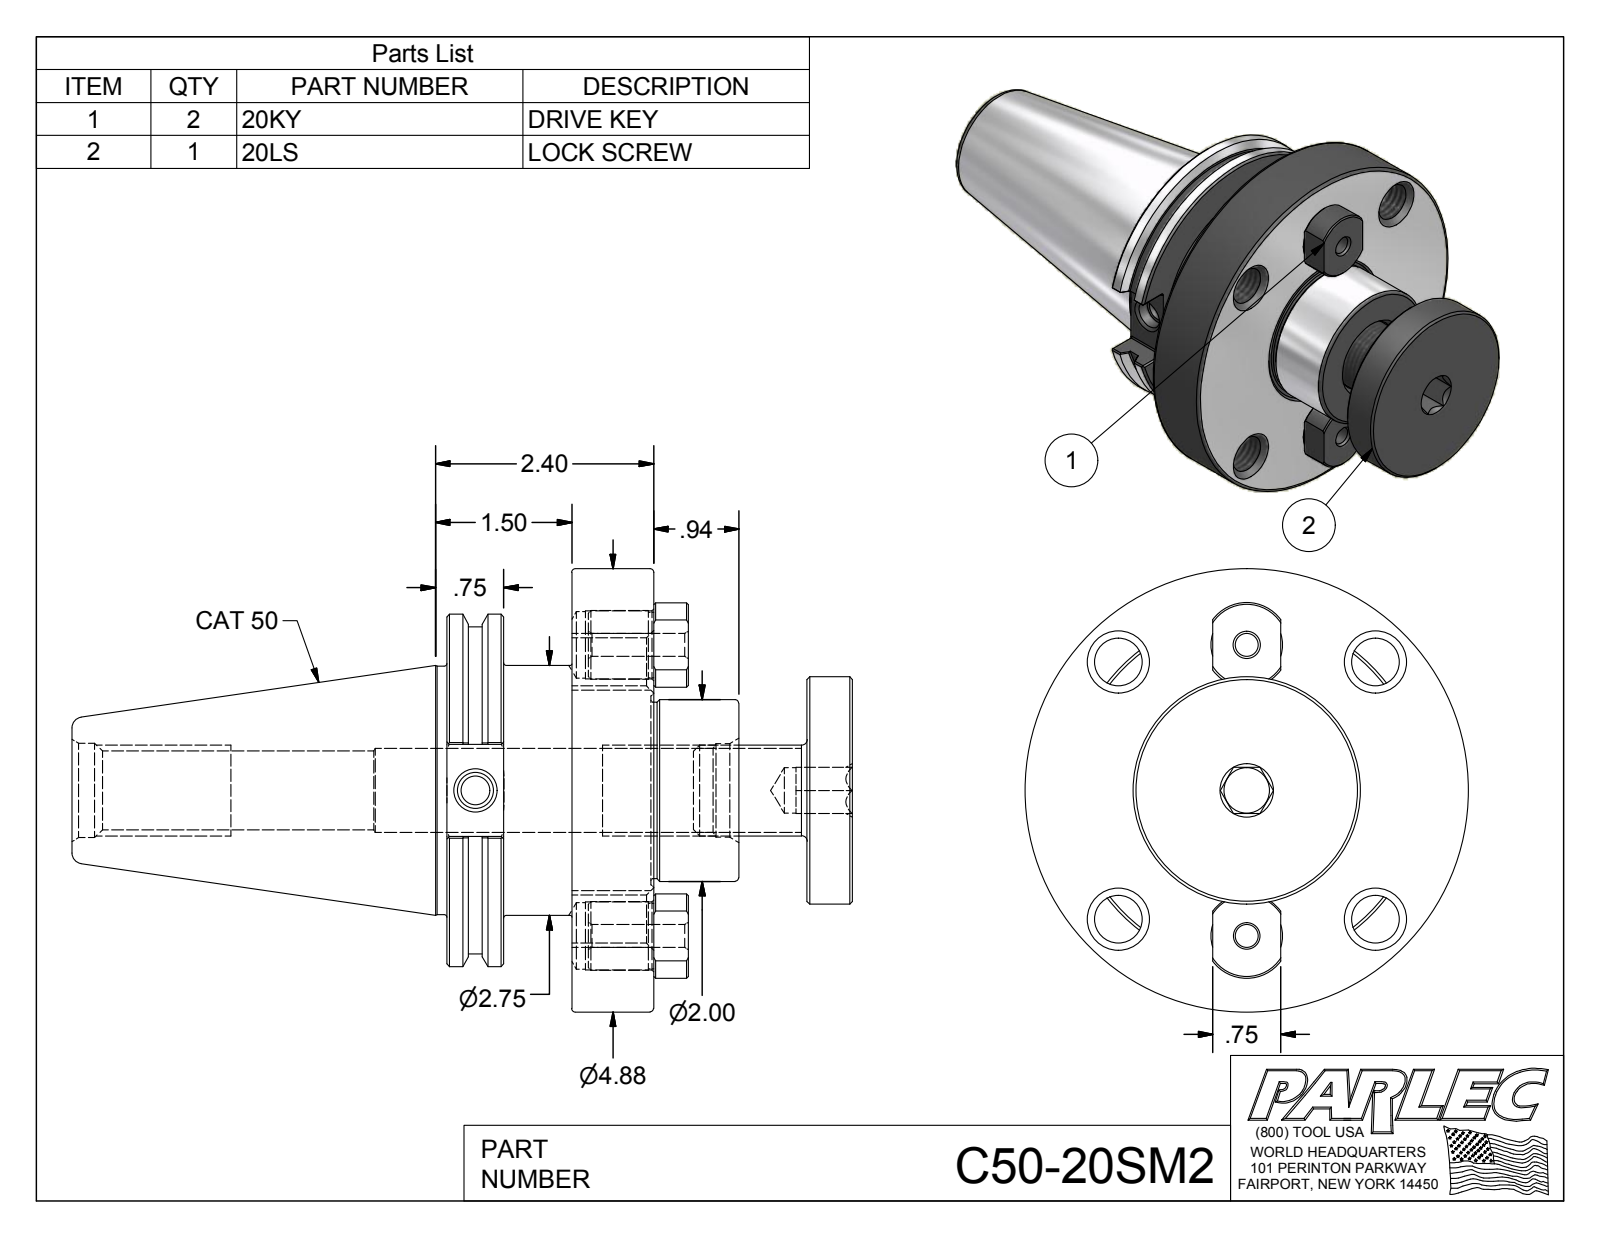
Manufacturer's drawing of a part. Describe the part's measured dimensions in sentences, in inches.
The part is named "C50-20SM2; C50-20SM2-1; 20KY; 20LS". Its 3-D file was written by "Autodesk Inventor 2012 (AUTOMOTIVE_DESIGN)". It is 4 solids with 172 faces: 58 planar, 50 cylindrical and 64 other. Overall it measures 8.587 by 4.875 by 4.875 inches. Its volume is 44.29 cubic inches and its surface area 161.8 square inches. Round holes: 4 of diameter 0.527, 2 of diameter 0.25, 2 of diameter 0.73, 2 of diameter 0.75, 1 of diameter 0.315, 1 of diameter 0.399, 1 of diameter 0.502, 1 of diameter 0.865, 1 of diameter 0.923, 1 of diameter 1.03, 1 of diameter 1.038. Round bosses or shafts: 2 of diameter 0.755, 2 of diameter 0.72, 1 of diameter 4.875, 1 of diameter 3.875, 1 of diameter 3.594, 1 of diameter 2.75, 1 of diameter 2.73, 1 of diameter 2.5. Partial cylindrical surfaces (rounded edges, fillets, slot ends): 12 of radius 0.02, 2 of radius 0.464. The main face-to-face distances are 0.9, 0.75, 2.587, 3.087, 2.187, 1.375, 2.275, 4.462, 1.65, 0.5. The hole center spacings are 1.426, 2, 2.828, 3.33, 1.6, 4, 3.2.
